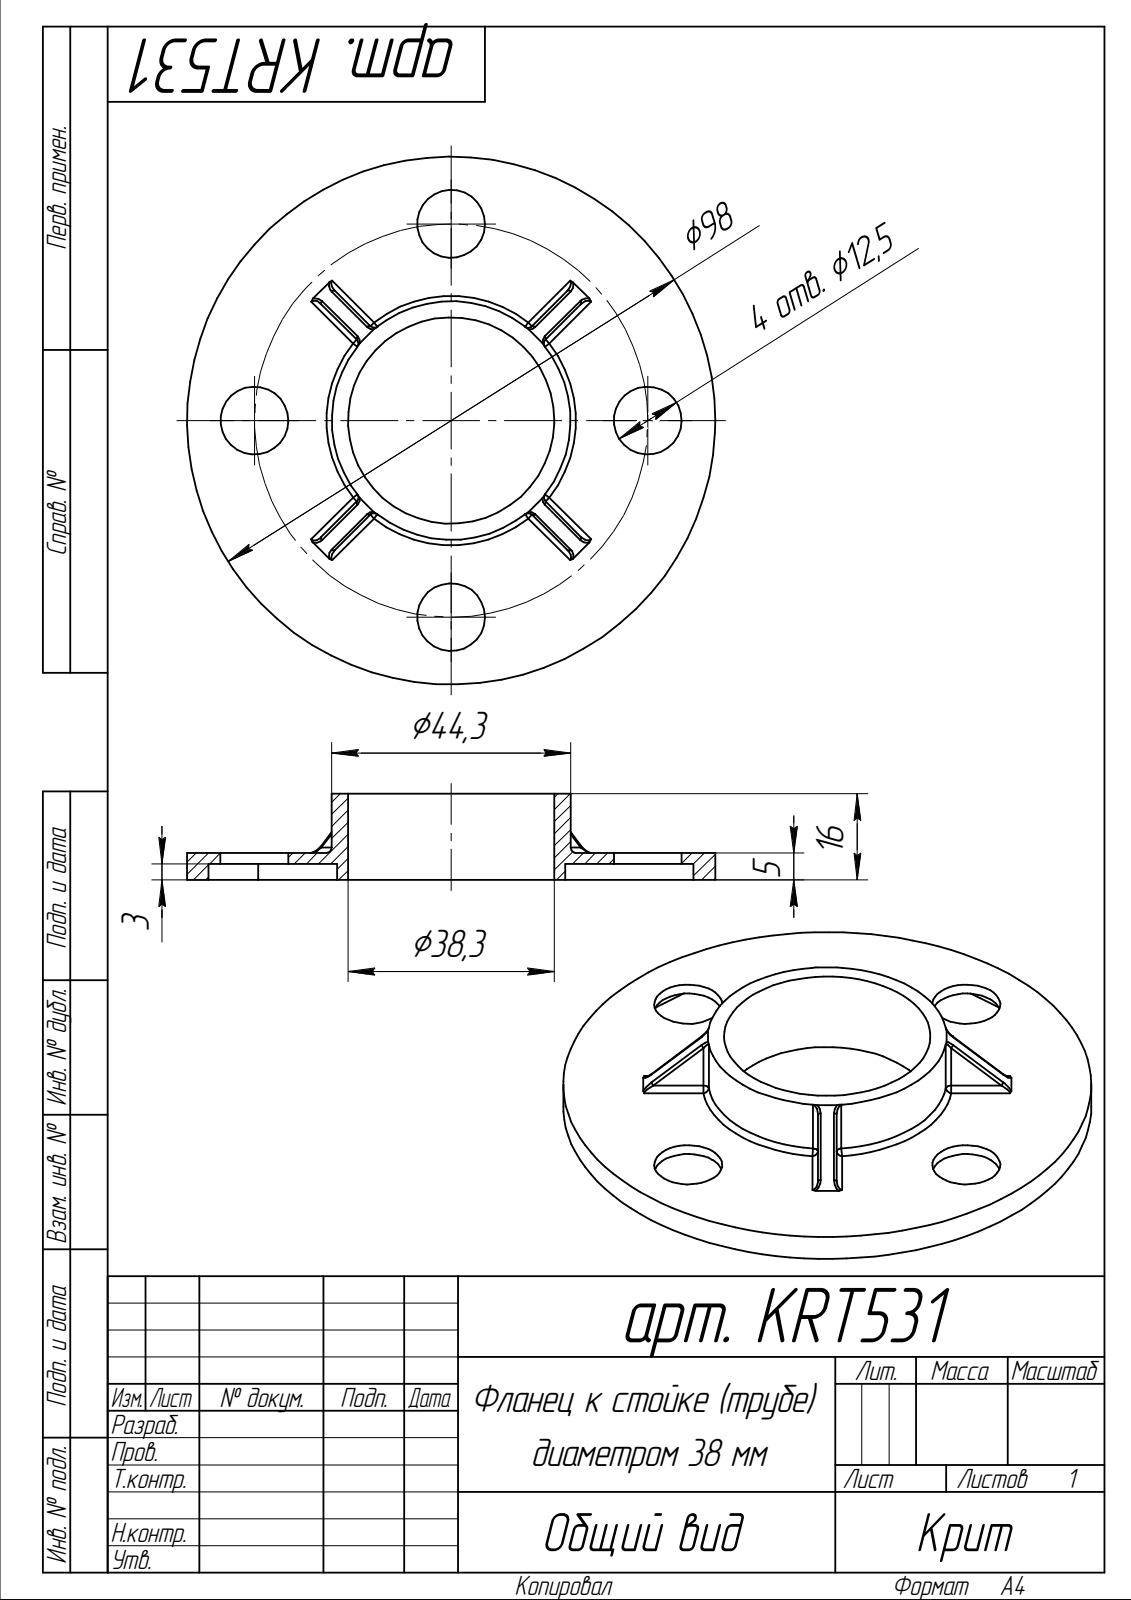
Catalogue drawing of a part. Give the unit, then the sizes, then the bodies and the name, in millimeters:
Units: millimetres
Overall size (bounding box): 98 × 98 × 16
Round holes (diameter × count): ⌀12.6 ×4, ⌀38.3 ×1, ⌀90 ×1
Round bosses / shafts (diameter × count): ⌀98 ×1, ⌀44.3 ×1, ⌀42.3 ×1
Partial cylindrical surfaces — rounded edges, fillets, slot ends (radius × count): R1 ×12, R0.5 ×8
Main face-to-face distances: 2, 3, 5, 16, 13, 11, 4.25, 7.75, 3.5, 12
Hole centre spacings: 36.5, 51.62, 73
Volume: 23 080 mm³ · Surface area: 18 782 mm²
Bodies: 1 solid, 101 faces (21 planar, 51 cylindrical, 29 other)
Part name (STEP PRODUCT): арт. KRT531
STEP written by: SolidWorks 2014 (AUTOMOTIVE_DESIGN)
